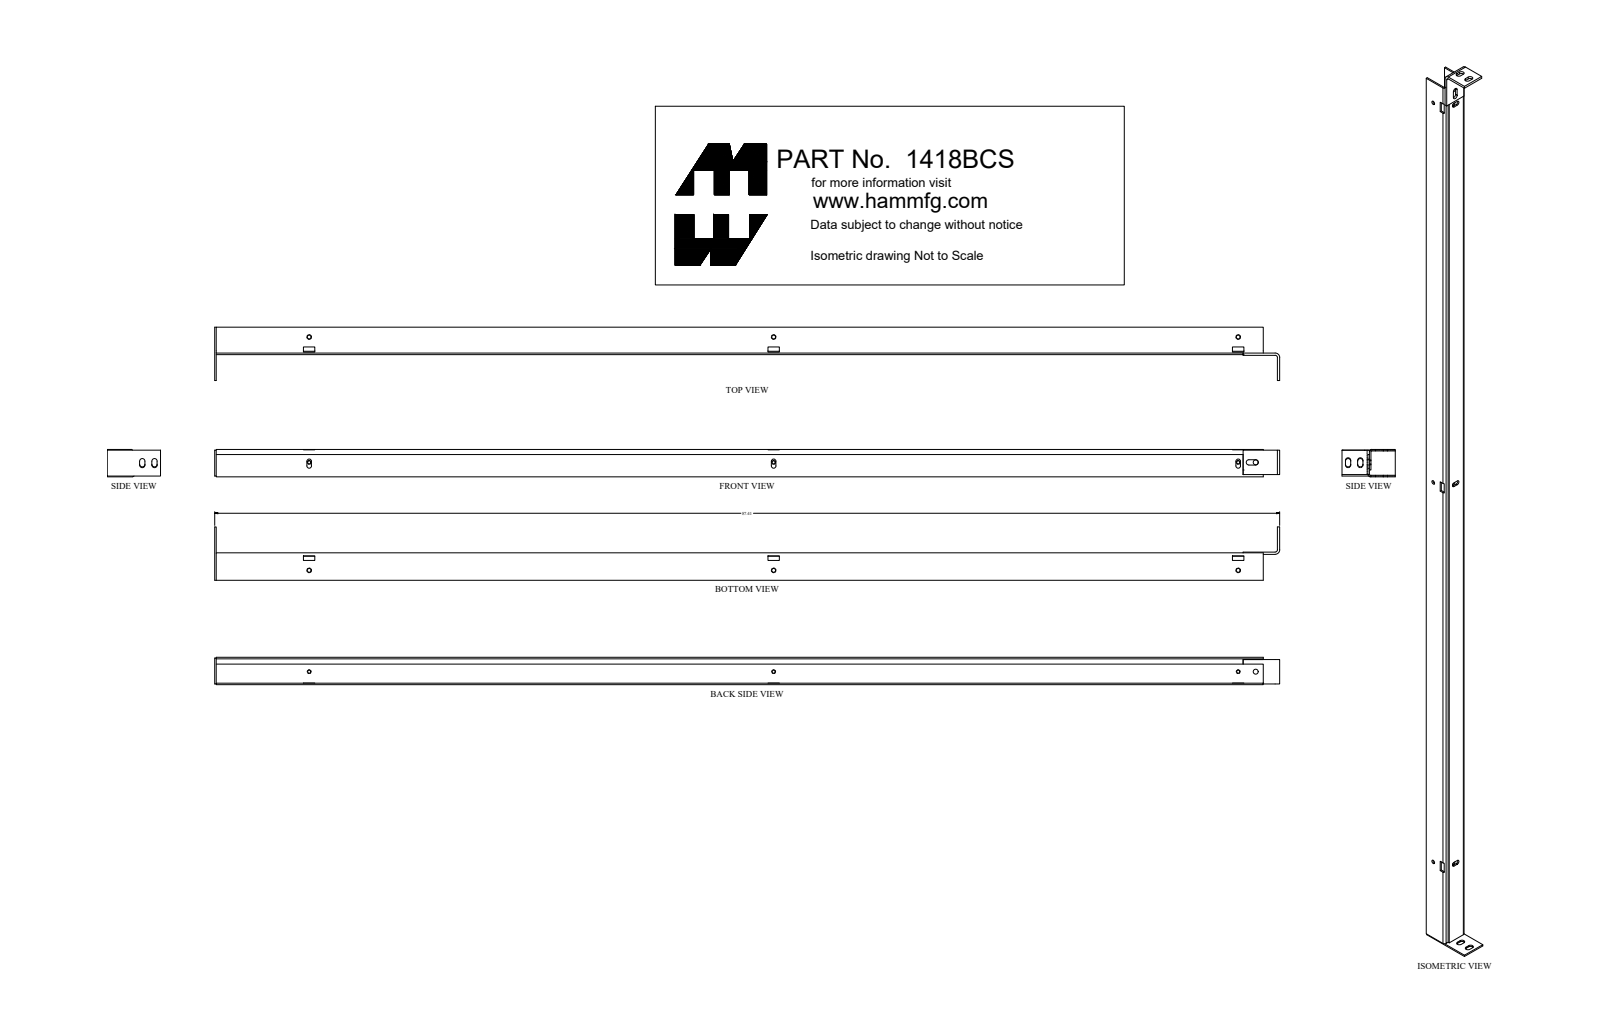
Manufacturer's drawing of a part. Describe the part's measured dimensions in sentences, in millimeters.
The part is named "1418BCS". Its 3-D file was written by "SolidWorks 2019 (AUTOMOTIVE_DESIGN)". It is 4 solids with 104 faces: 72 planar, 32 cylindrical and 0 other. Overall it measures 2220.9 by 111.1 by 57.1 millimeters. Its volume is 1 350 000 cubic millimeters and its surface area 884 500 square millimeters. Round holes: 3 of diameter 7.2, 3 of diameter 8.7, 1 of diameter 10.3. Partial cylindrical surfaces (rounded edges, fillets, slot ends): 8 of radius 5.6, 3 of radius 1.5, 3 of radius 4.7, 3 of radius 4.7, 3 of radius 4.8, 2 of radius 6.4. The main face-to-face distances are 3.2, 3.2, 57.1, 53.9, 53.9, 50.7, 6.4, 54, 50.8, 57.2. The hole center spacings are 968.4, 968.4, 1936.8, 36.5, 1004.9, 1973.3.
